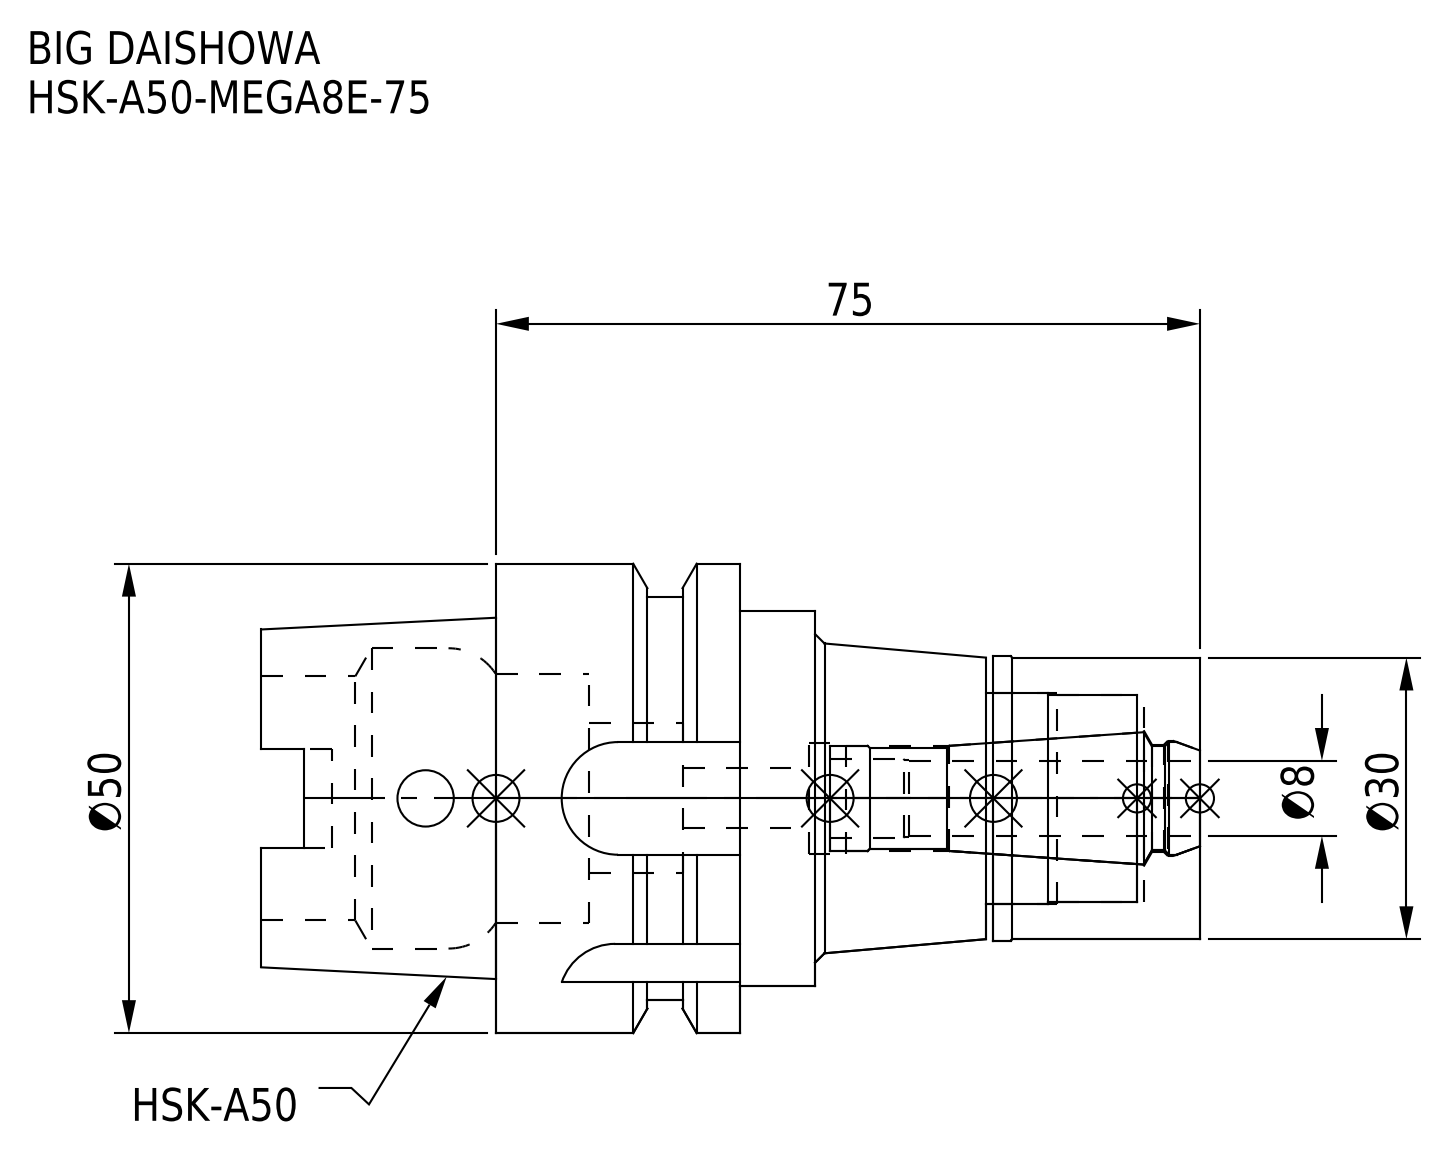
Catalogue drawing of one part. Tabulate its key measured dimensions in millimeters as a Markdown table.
| quantity | value |
| --- | --- |
| part name | HSK-A50-MEGA8E-75-080.stp; HA50ME08075-080_ASM.stp; HSK-A50-MEGA8E-75-080-FreeParts; HSK-A50-MEGA8E-75_1.stp (+3 more) |
| STEP written by | SolidWorks 2019 (CONFIG_CONTROL_DESIGN) |
| units | millimeters |
| bodies | 2 solids, 126 faces (45 planar, 53 cylindrical, 28 other) |
| overall size | 100 × 50 × 50 |
| volume | 84 116 mm³ |
| surface area | 24 965 mm² |
| round holes (diameter × count) | 6 × 1, 6.4 × 1, 11.2 × 1, 11.4 × 1, 11.8 × 1, 12.3 × 1, 16 × 1, 22 × 1, 22.5 × 1, 26 × 1, 26.6 × 1, 32 × 1 |
| round bosses / shafts (diameter × count) | 50 × 1, 43 × 1, 40 × 1, 30.3 × 1, 30 × 1 |
| partial cylindrical surfaces (radius × count) | 2.38 × 4, 6 × 4 |
| main face-to-face distances | 75, 49, 26, 65.05, 16.05, 9.95, 27, 22, 43.05, 53 |
